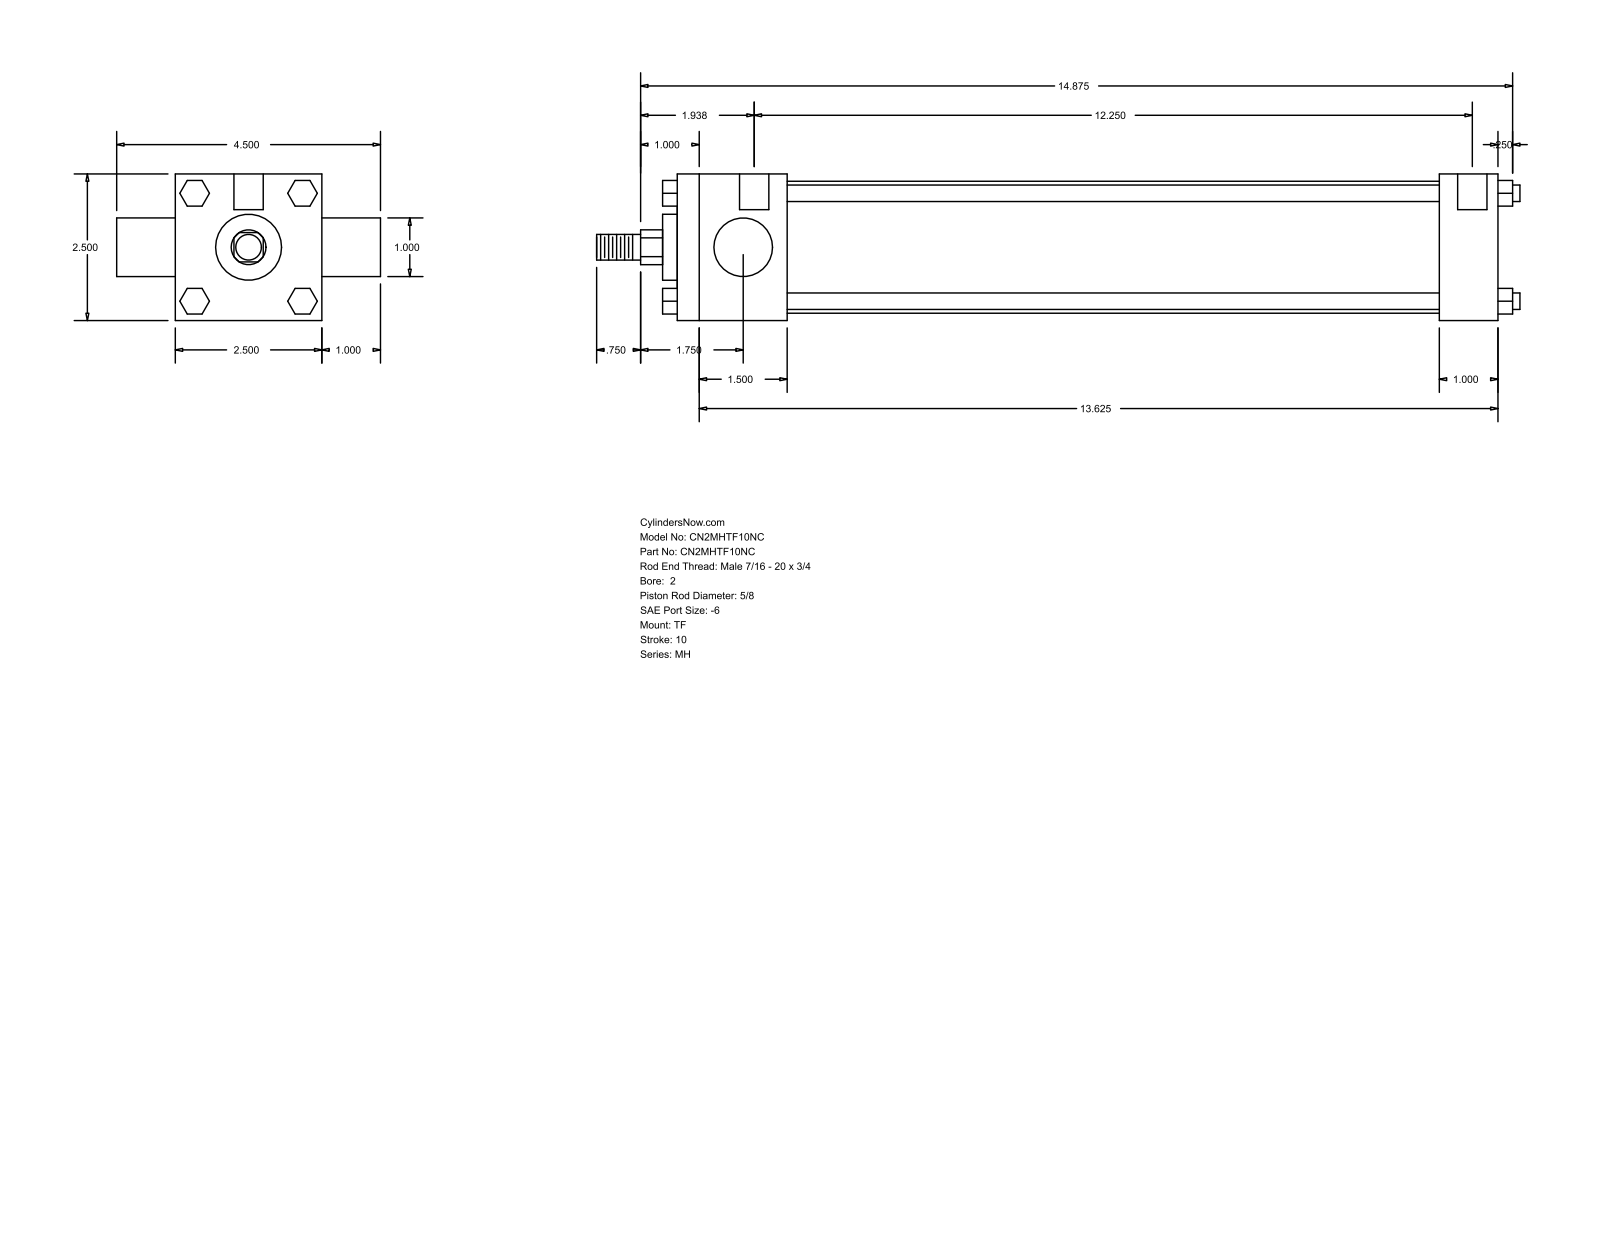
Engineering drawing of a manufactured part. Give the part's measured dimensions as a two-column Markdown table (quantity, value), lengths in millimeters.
| quantity | value |
| --- | --- |
| part name | MH_TF__0200_0.625 |
| STEP written by | GSSL Pune (CONFIG_CONTROL_DESIGN) |
| units | millimeters |
| bodies | 0 solids, 120 faces (92 planar, 28 cylindrical, 0 other) |
| overall size | 400.05 × 114.3 × 63.5 |
| round holes (diameter × count) | 5.56 × 3, 12.7 × 2 |
| round bosses / shafts (diameter × count) | 7.14 × 4, 57.15 × 1, 28.57 × 1, 25.4 × 1, 15.88 × 1, 11.11 × 1 |
| partial cylindrical surfaces (radius × count) | 7.54 × 1 |
| main face-to-face distances | 63.5, 355.6, 47.62, 330.19, 282.57, 307.98, 25.41, 25.4, 88.9, 6.35 |
| hole center spacings | 3.18, 4.76, 311.15, 314.33, 315.91, 319.09 |
